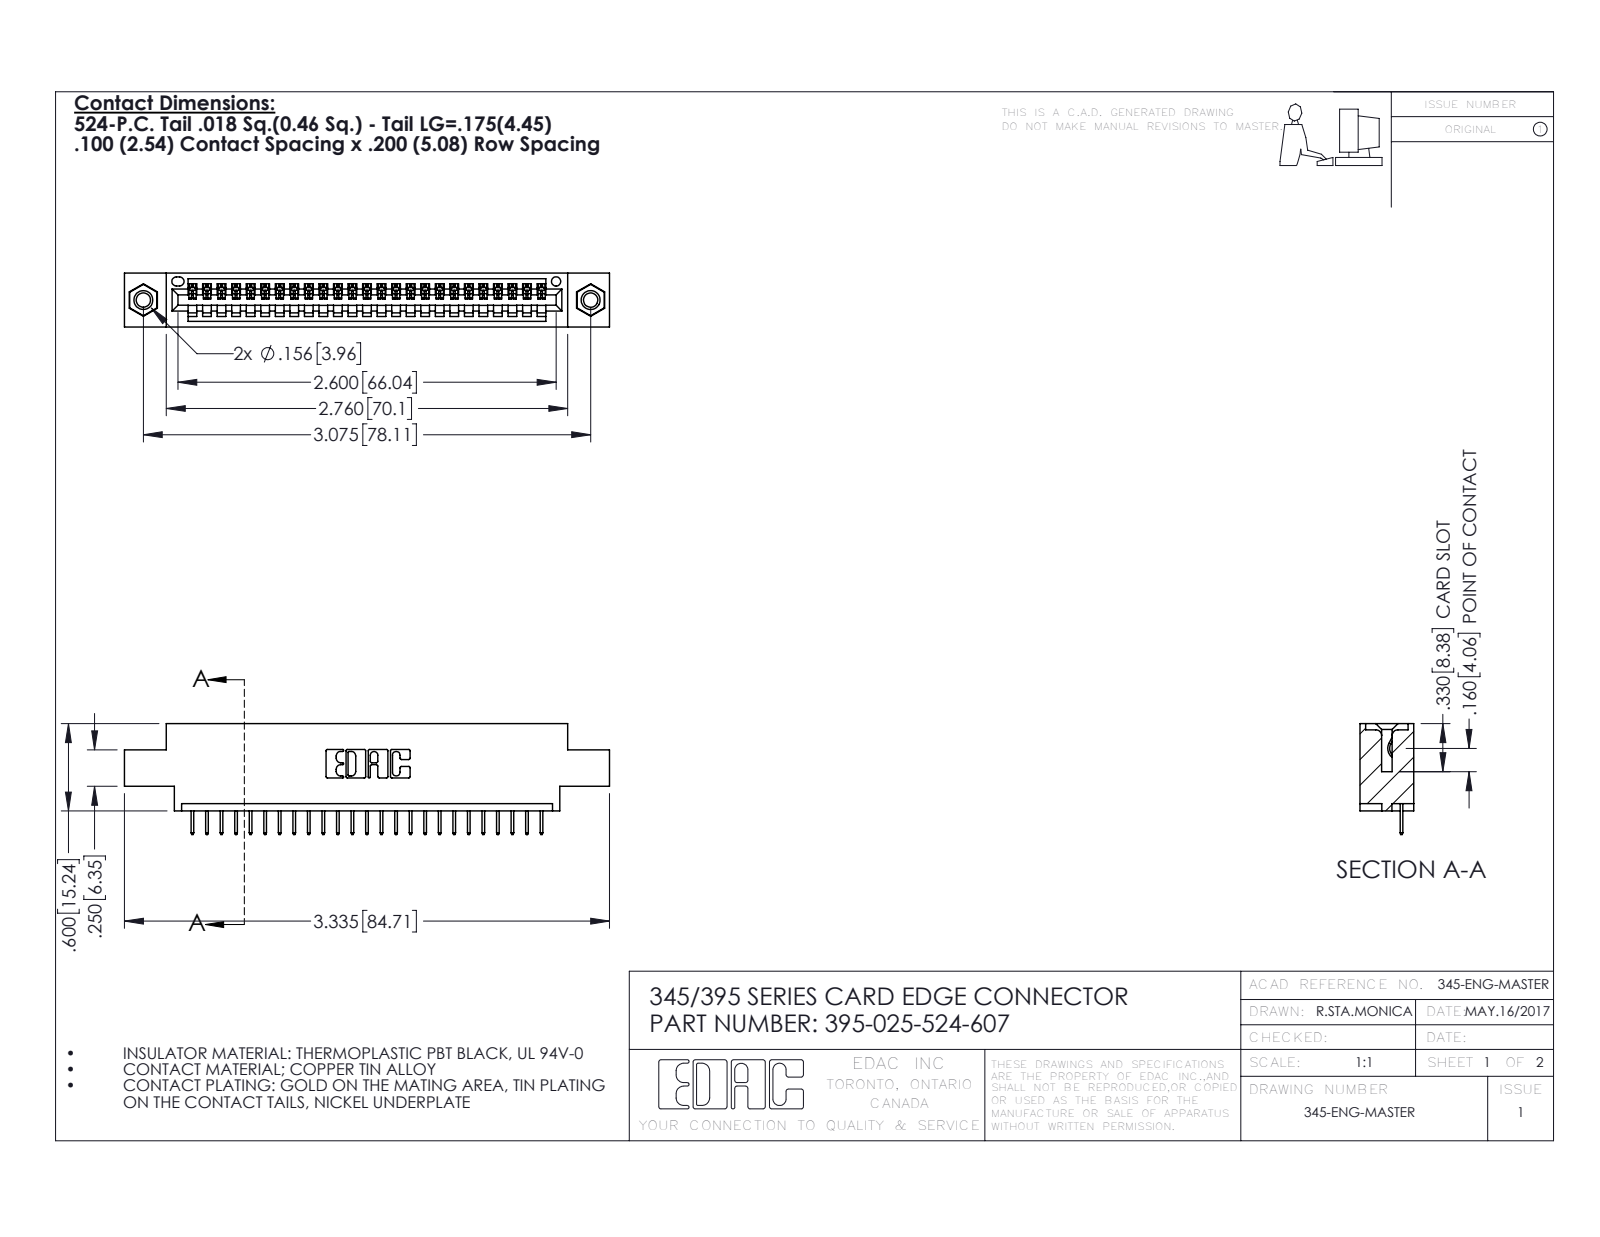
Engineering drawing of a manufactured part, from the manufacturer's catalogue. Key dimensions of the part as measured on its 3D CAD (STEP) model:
Part name (STEP PRODUCT): 395-025-524-607; 345-292-001_345-293-124; 345 Part_0.170 Offset - 0.156 Dia-TI; 345-250-001_345-250-005-103
STEP written by: SolidWorks 2016 (CONFIG_CONTROL_DESIGN)
Units: inches
Bodies: 28 solids, 1740 faces (1266 planar, 458 cylindrical, 16 other)
Overall size (bounding box): 3.335 × 0.762 × 0.37
Volume: 0.469 in³ · Surface area: 15.22 in²
Round holes (diameter × count): ⌀0.098 ×2, ⌀0.125 ×2, ⌀0.156 ×2, ⌀0.064 ×1
Round bosses / shafts (diameter × count): ⌀0.155 ×2
Partial cylindrical surfaces — rounded edges, fillets, slot ends (radius × count): R0.006 ×50, R0.01 ×22, R0.007 ×6, R0.031 ×6, R0.026 ×3, R0.031 ×2, R0.04 ×2, R0.014 ×1
Main face-to-face distances: 0.072, 0.298, 0.37, 0.2, 0.098, 0.272, 0.025, 0.225, 0.072, 0.175
Hole centre spacings: 0.27, 2.84, 3.075
